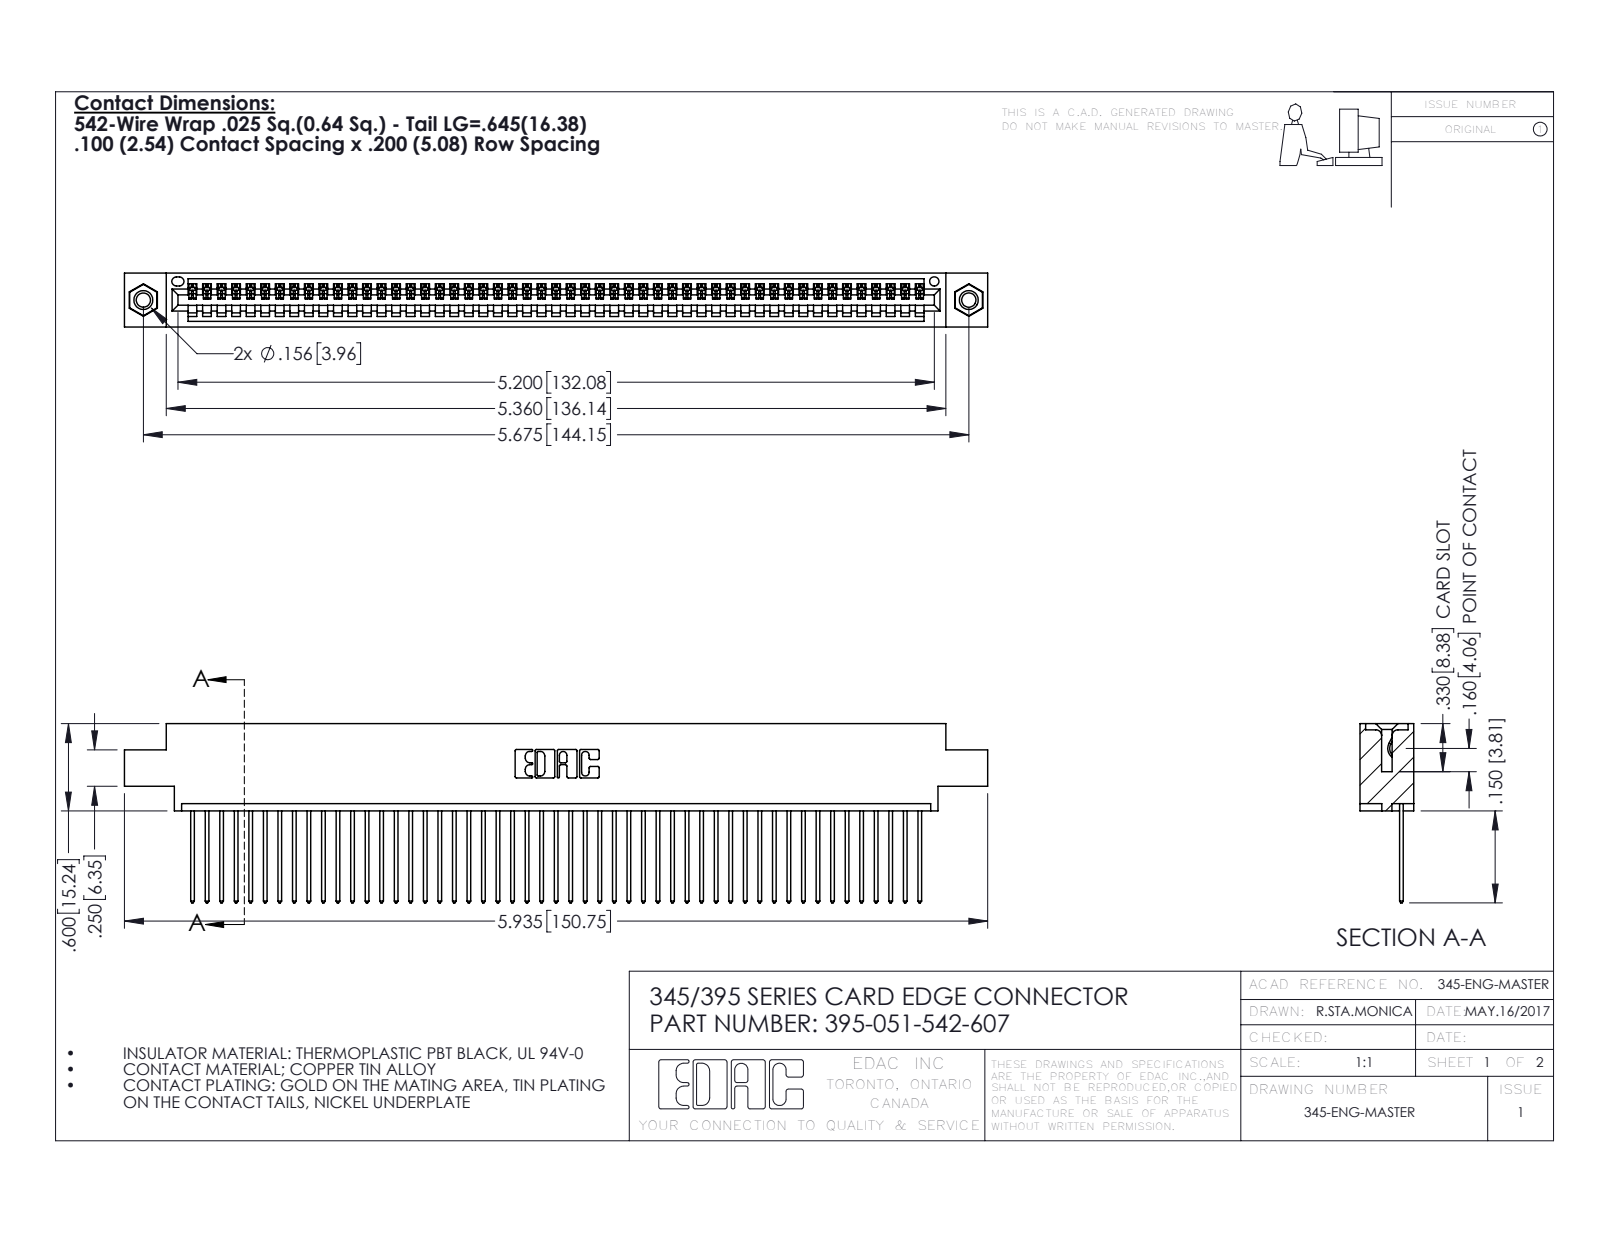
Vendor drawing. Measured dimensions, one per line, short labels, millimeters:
name: 345 Part_0.170 Offset - 0.156 Dia-TI; 345-250-001_345-250-005-103; 345-292-001_345-293-142; 395-051-542-607
written by: SolidWorks 2016 (CONFIG_CONTROL_DESIGN)
unit: mm
bodies: 54 solids, 3148 faces (2156 planar, 976 cylindrical, 16 other)
size: 150.7 × 31.3 × 9.4
volume: 14 400 mm³; area: 20 110 mm²
holes: 2× ⌀2.5, 2× ⌀3.2, 2× ⌀4, 1× ⌀1.6
bosses: 2× ⌀3.9
rounds: 102× R0.2, 102× R0.3, 22× R0.3, 6× R0.2, 6× R0.8, 3× R0.7, 2× R0.8, 2× R1
face distances: 1.8, 7.6, 9.4, 2.5, 6.9, 0.6, 5.1, 5.7, 4.4, 3.8
hole spacings: 6.9, 138.2, 144.1
